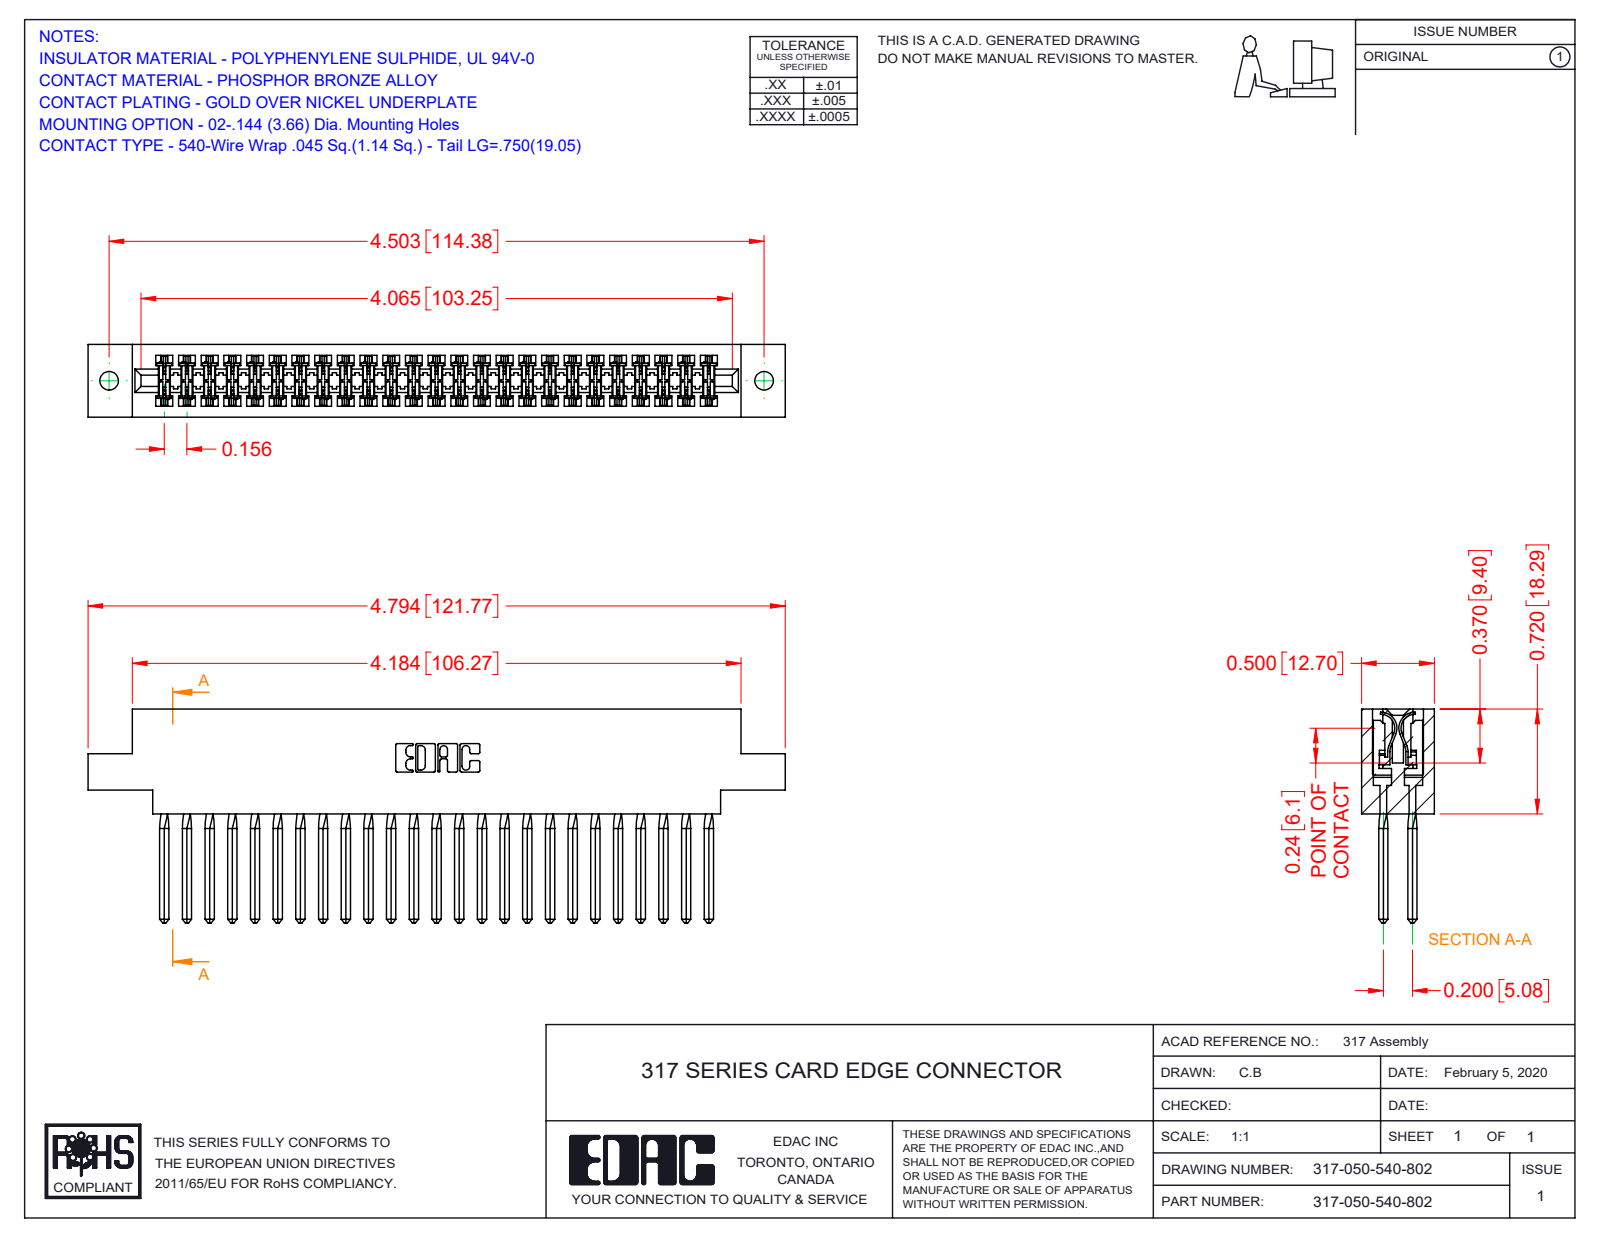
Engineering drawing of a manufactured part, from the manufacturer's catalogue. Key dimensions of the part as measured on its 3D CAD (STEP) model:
Part name (STEP PRODUCT): 317-050-540-802; 317-290-001_540; 317 Part_.144 Dia
STEP written by: SolidWorks 2016 (CONFIG_CONTROL_DESIGN)
Units: inches
Bodies: 51 solids, 4552 faces (3708 planar, 644 cylindrical, 200 other)
Overall size (bounding box): 4.794 × 1.47 × 0.5
Volume: 1.21 in³ · Surface area: 44.41 in²
Round holes (diameter × count): ⌀0.128 ×2
Partial cylindrical surfaces — rounded edges, fillets, slot ends (radius × count): R0.015 ×100, R0.01 ×22, R0.007 ×6, R0.031 ×6, R0.026 ×3, R0.095 ×2, R0.1 ×2, R0.11 ×2
Main face-to-face distances: 0.5, 0.075, 0.425, 0.35, 0.11, 0.195, 0.094, 0.72, 0.2, 0.115
Hole centre spacings: 4.503
